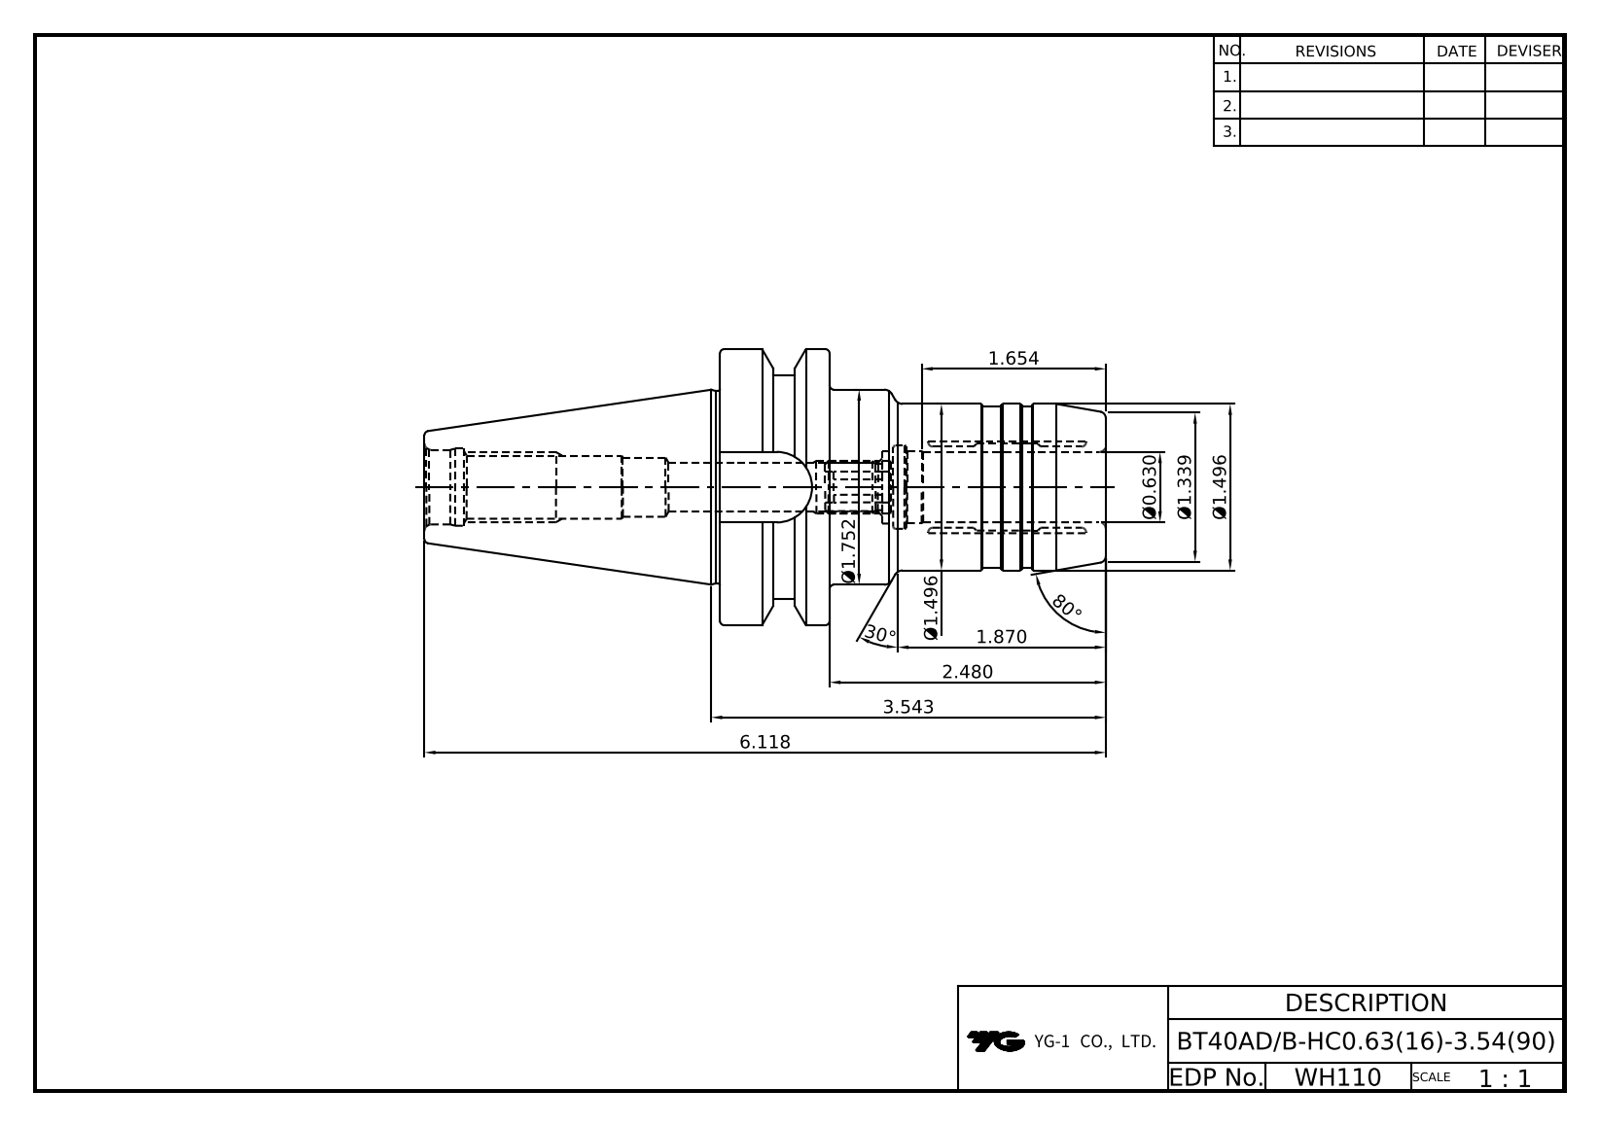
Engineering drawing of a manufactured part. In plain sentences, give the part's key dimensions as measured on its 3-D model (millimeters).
The part is named "LO-BT40ADB-HC16-90". Its 3-D file was written by "CREO PARAMETRIC BY PTC INC, 2018100 (CONFIG_CONTROL_DESIGN)". It is 1 solid with 174 faces: 30 planar, 70 cylindrical and 74 other. Overall it measures 155.4 by 63 by 63 millimeters. Its volume is 183 631 cubic millimeters and its surface area 35 011 square millimeters. Round holes: 5 of diameter 4, 3 of diameter 3.4, 2 of diameter 4.2, 1 of diameter 12, 1 of diameter 13.5, 1 of diameter 14, 1 of diameter 16, 1 of diameter 16.6, 1 of diameter 17, 1 of diameter 17.6. Round bosses or shafts: 1 of diameter 63, 1 of diameter 51, 1 of diameter 44.5, 1 of diameter 44, 1 of diameter 38, 1 of diameter 37. Partial cylindrical surfaces (rounded edges, fillets, slot ends): 1 of radius 8.05. The main face-to-face distances are 25, 88, 63, 45.2, 17.1, 7.9, 70.9, 12.1, 5, 12.9.
